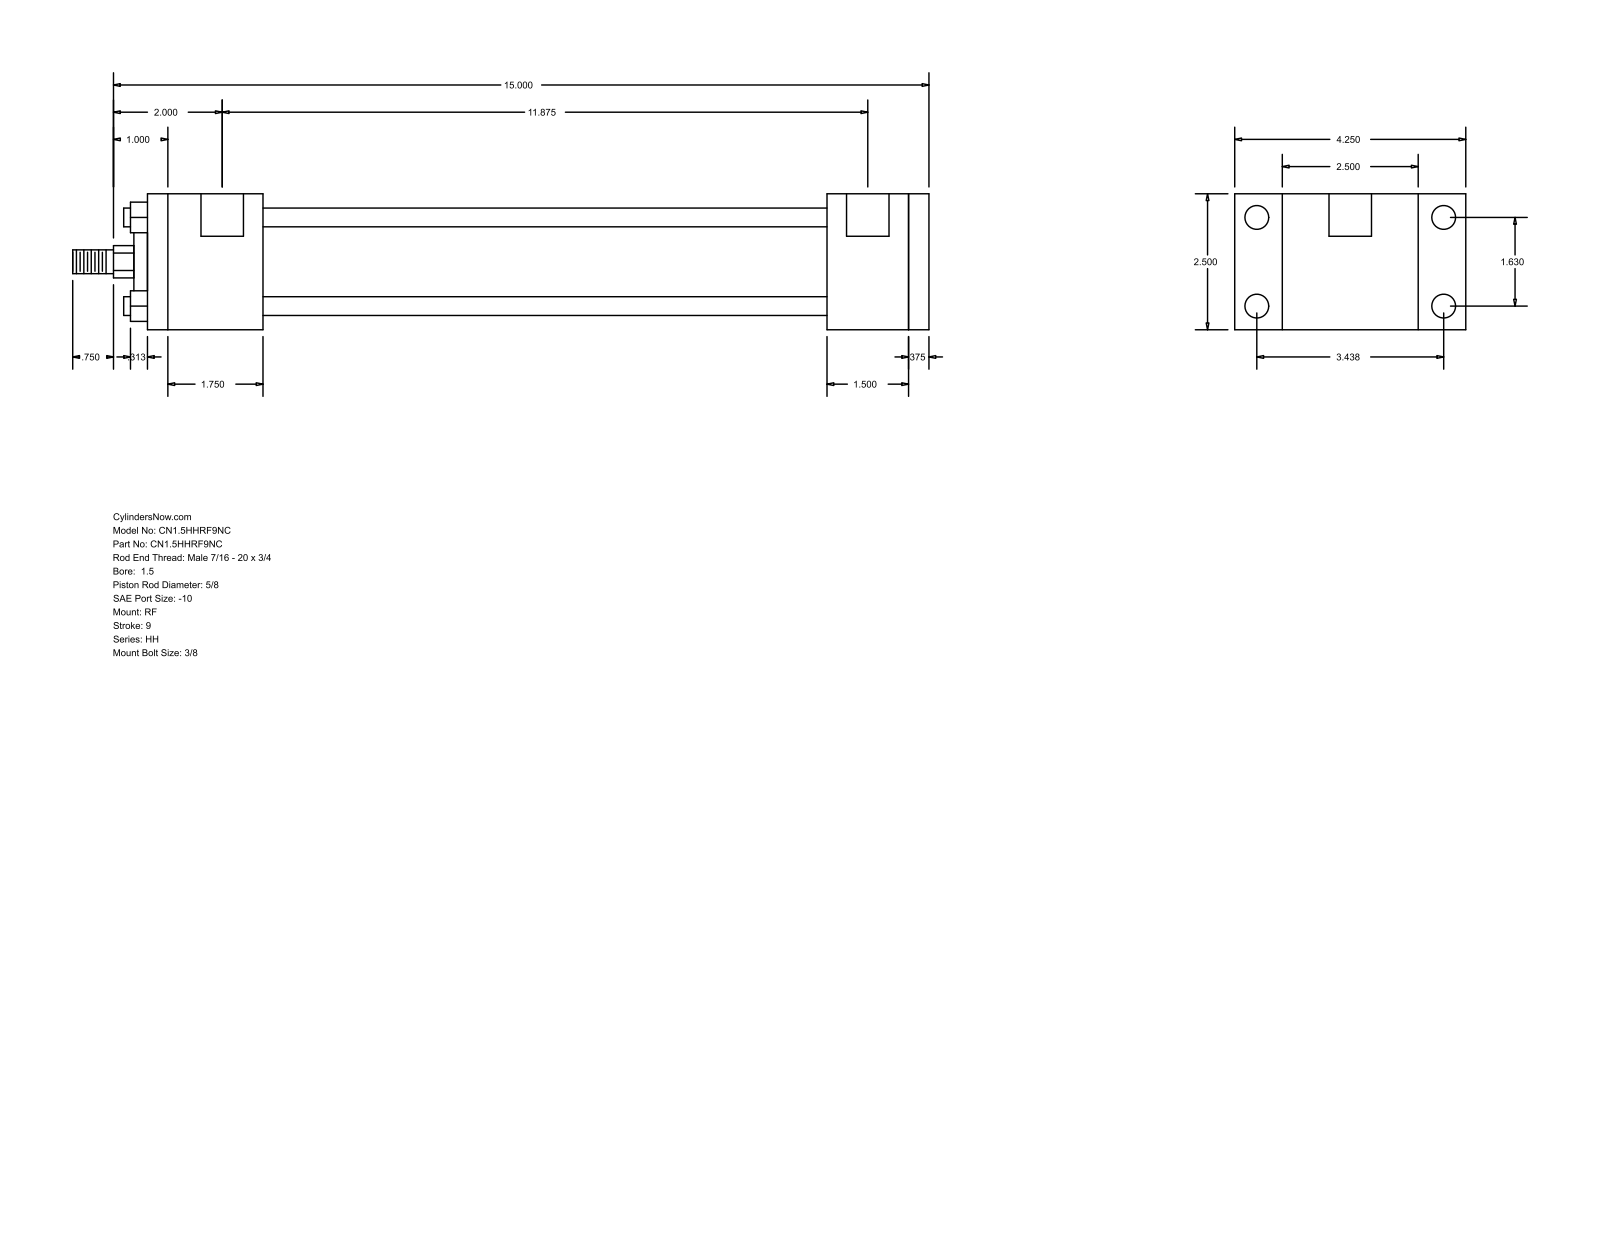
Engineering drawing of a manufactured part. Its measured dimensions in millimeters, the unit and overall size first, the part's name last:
Units: millimetres
Overall size (bounding box): 400.05 × 107.95 × 63.5
Round holes (diameter × count): ⌀5.56 ×4, ⌀11.13 ×4, ⌀19.84 ×2
Round bosses / shafts (diameter × count): ⌀8.76 ×4, ⌀44.45 ×1, ⌀28.57 ×1, ⌀15.88 ×1, ⌀11.11 ×1
Partial cylindrical surfaces — rounded edges, fillets, slot ends (radius × count): R7.54 ×1
Main face-to-face distances: 63.5, 365.12, 38.1, 355.6, 9.52, 53.97, 317.5, 263.53, 301.63, 311.15
Hole centre spacings: 41.4, 87.32, 96.64, 304.8, 1.58, 1.59, 301.63, 303.21
Bodies: 0 solids, 92 faces (64 planar, 28 cylindrical, 0 other)
Part name (STEP PRODUCT): HH_RF__0150_0.625
STEP written by: GSSL Pune (CONFIG_CONTROL_DESIGN)
